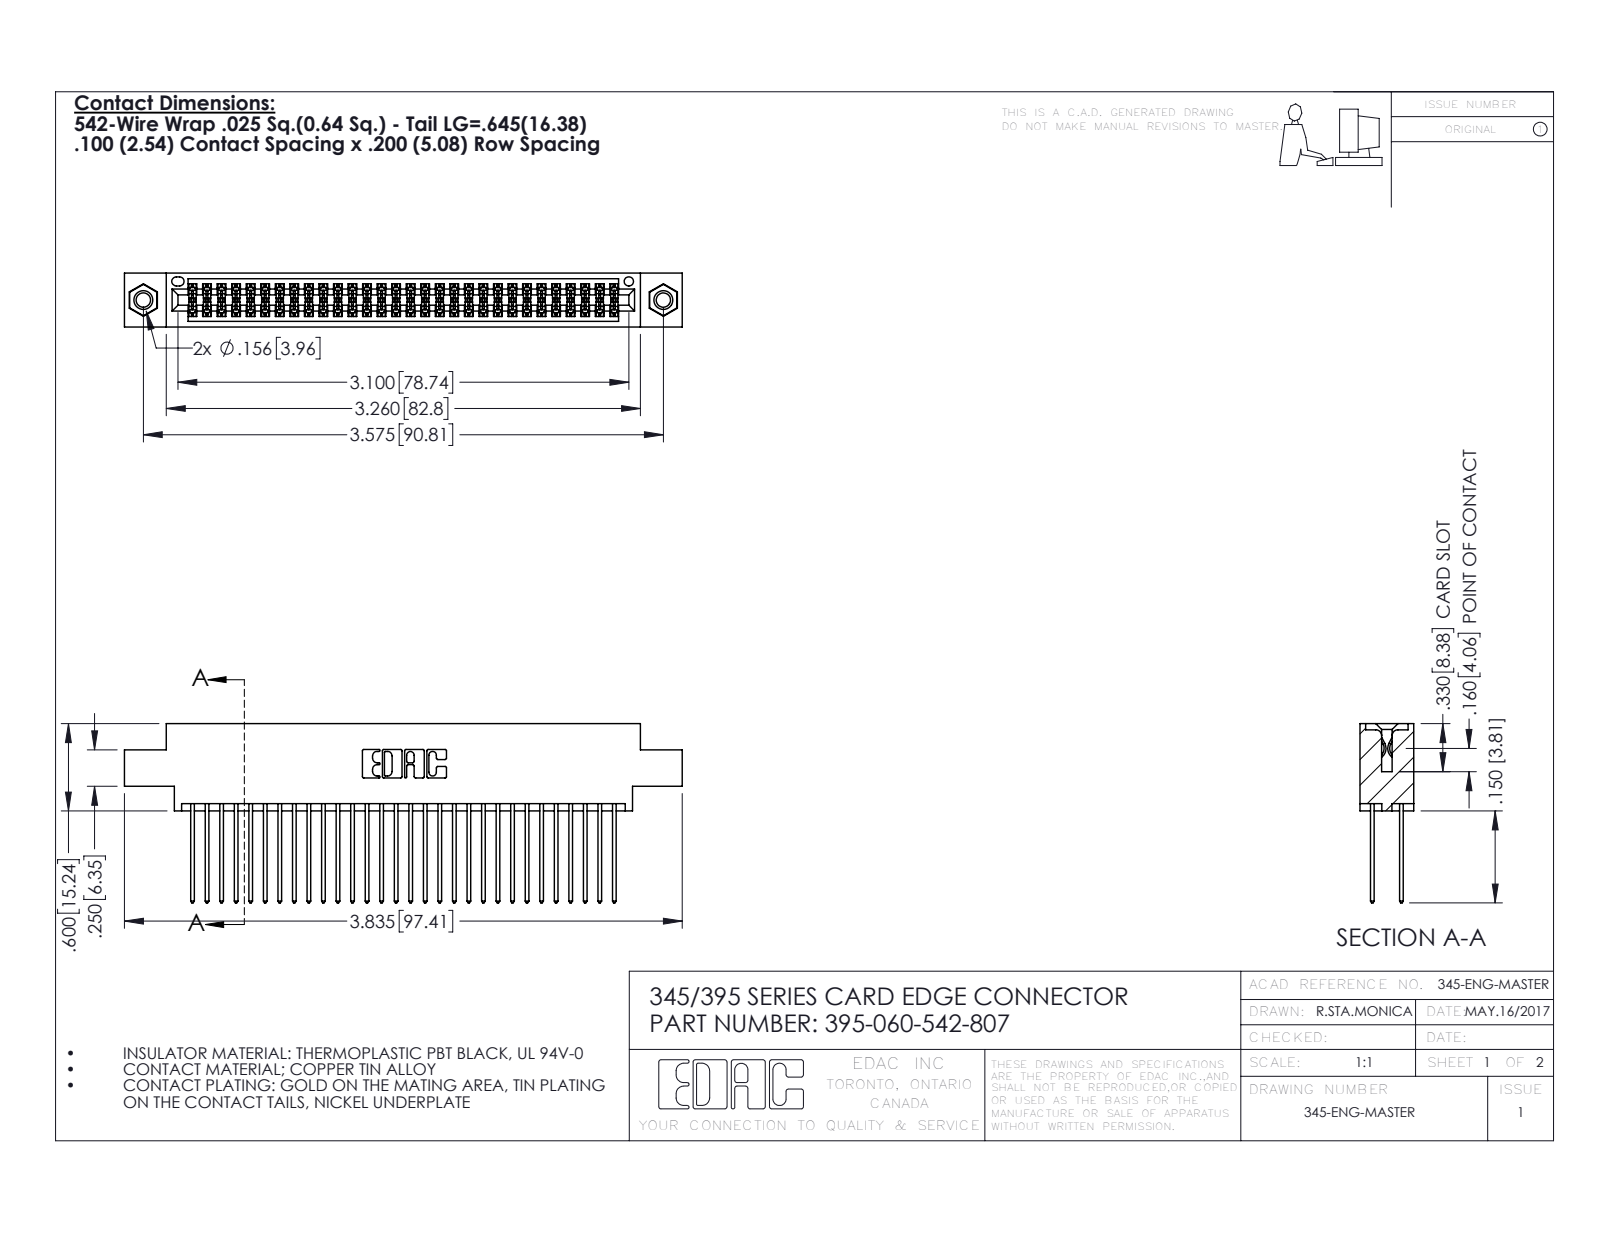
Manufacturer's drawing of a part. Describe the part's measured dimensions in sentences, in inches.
The part is named "395-060-542-807; 345 Part_0.170 Offset - 0.156 Dia-TI; 345-250-001_345-250-005-103; 345-292-001_345-293-142". Its 3-D file was written by "SolidWorks 2016 (CONFIG_CONTROL_DESIGN)". It is 63 solids with 3190 faces: 2096 planar, 1078 cylindrical and 16 other. Overall it measures 3.835 by 1.232 by 0.37 inches. Its volume is 0.58 cubic inches and its surface area 23.71 square inches. Round holes: 2 of diameter 0.098, 2 of diameter 0.125, 2 of diameter 0.156, 1 of diameter 0.064. Round bosses or shafts: 2 of diameter 0.155. Partial cylindrical surfaces (rounded edges, fillets, slot ends): 90 of radius 0.006, 60 of radius 0.01, 22 of radius 0.01, 6 of radius 0.007, 6 of radius 0.031, 3 of radius 0.026, 2 of radius 0.014, 2 of radius 0.019. The main face-to-face distances are 0.072, 0.298, 0.2, 0.098, 0.272, 0.025, 0.37, 0.225, 0.175, 0.149. The hole center spacings are 0.27, 3.34, 3.575.
